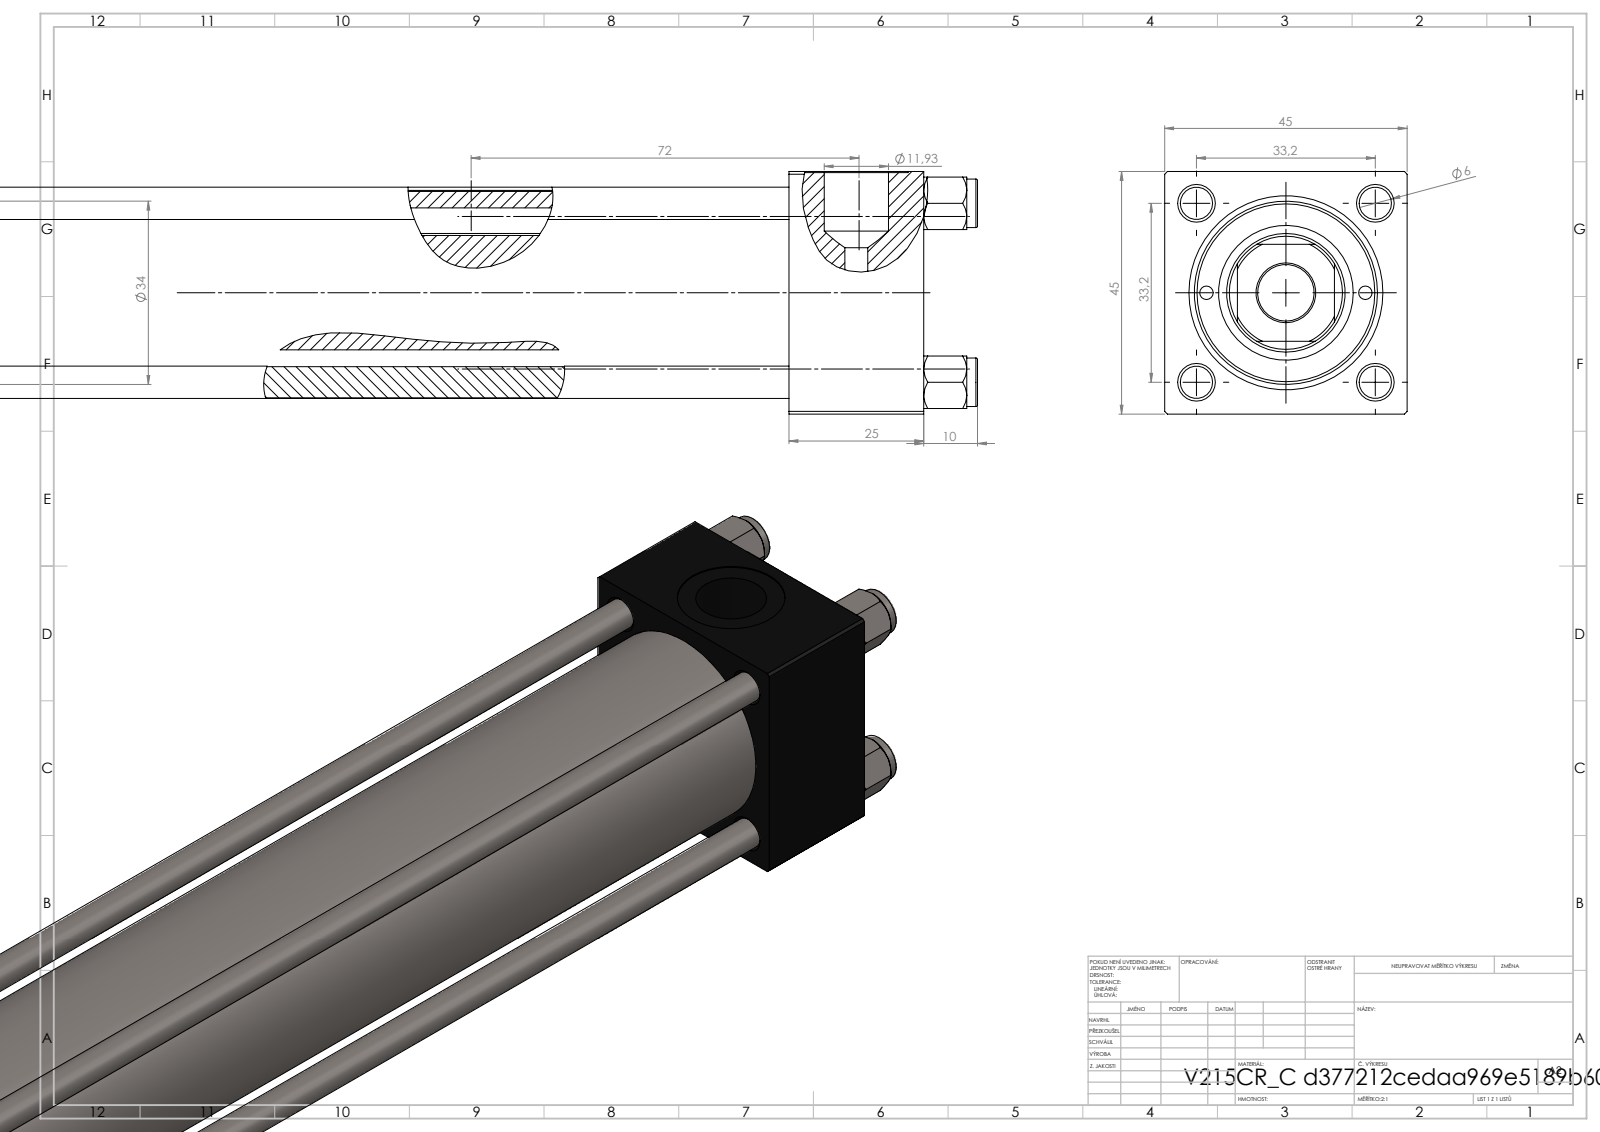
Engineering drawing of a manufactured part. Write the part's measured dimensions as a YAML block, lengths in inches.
part_name: "V215CR_C_TYCINKA; V215CR_VCP_C; V215_VC_A; NUT_M5_C (+1 more)"
step_written_by: "SolidWorks 2019 (CONFIG_CONTROL_DESIGN)"
units: inches
bodies: {solids: 11, faces: 1154, planar: 527, cylindrical: 91, other: 536}
overall_size: [13.307, 1.772, 1.772]
volume: 21.83
surface_area: 212.6
round_holes:
  - {diameter: 0.236, count: 4}
  - {diameter: 0.098, count: 2}
  - {diameter: 0.276, count: 2}
  - {diameter: 0.518, count: 2}
  - {diameter: 0.787, count: 2}
  - {diameter: 0.413, count: 1}
  - {diameter: 0.866, count: 1}
  - {diameter: 0.945, count: 1}
  - {diameter: 0.984, count: 1}
  - {diameter: 1.26, count: 1}
  - {diameter: 1.299, count: 1}
round_bosses_or_shafts:
  - {diameter: 0.354, count: 4}
  - {diameter: 1.496, count: 1}
  - {diameter: 1.339, count: 1}
partial_cylinders:
  - {radius: 0.413, count: 1}
face_to_face_distances: [1.772, 0.984, 11.929, 10.039, 9.055, 10.945, 1.89, 10.799, 9.815, 0.76]
hole_center_spacings: [0.657, 0.924, 1.307, 1.396, 0.581, 1.848, 1.161, 10.059]
